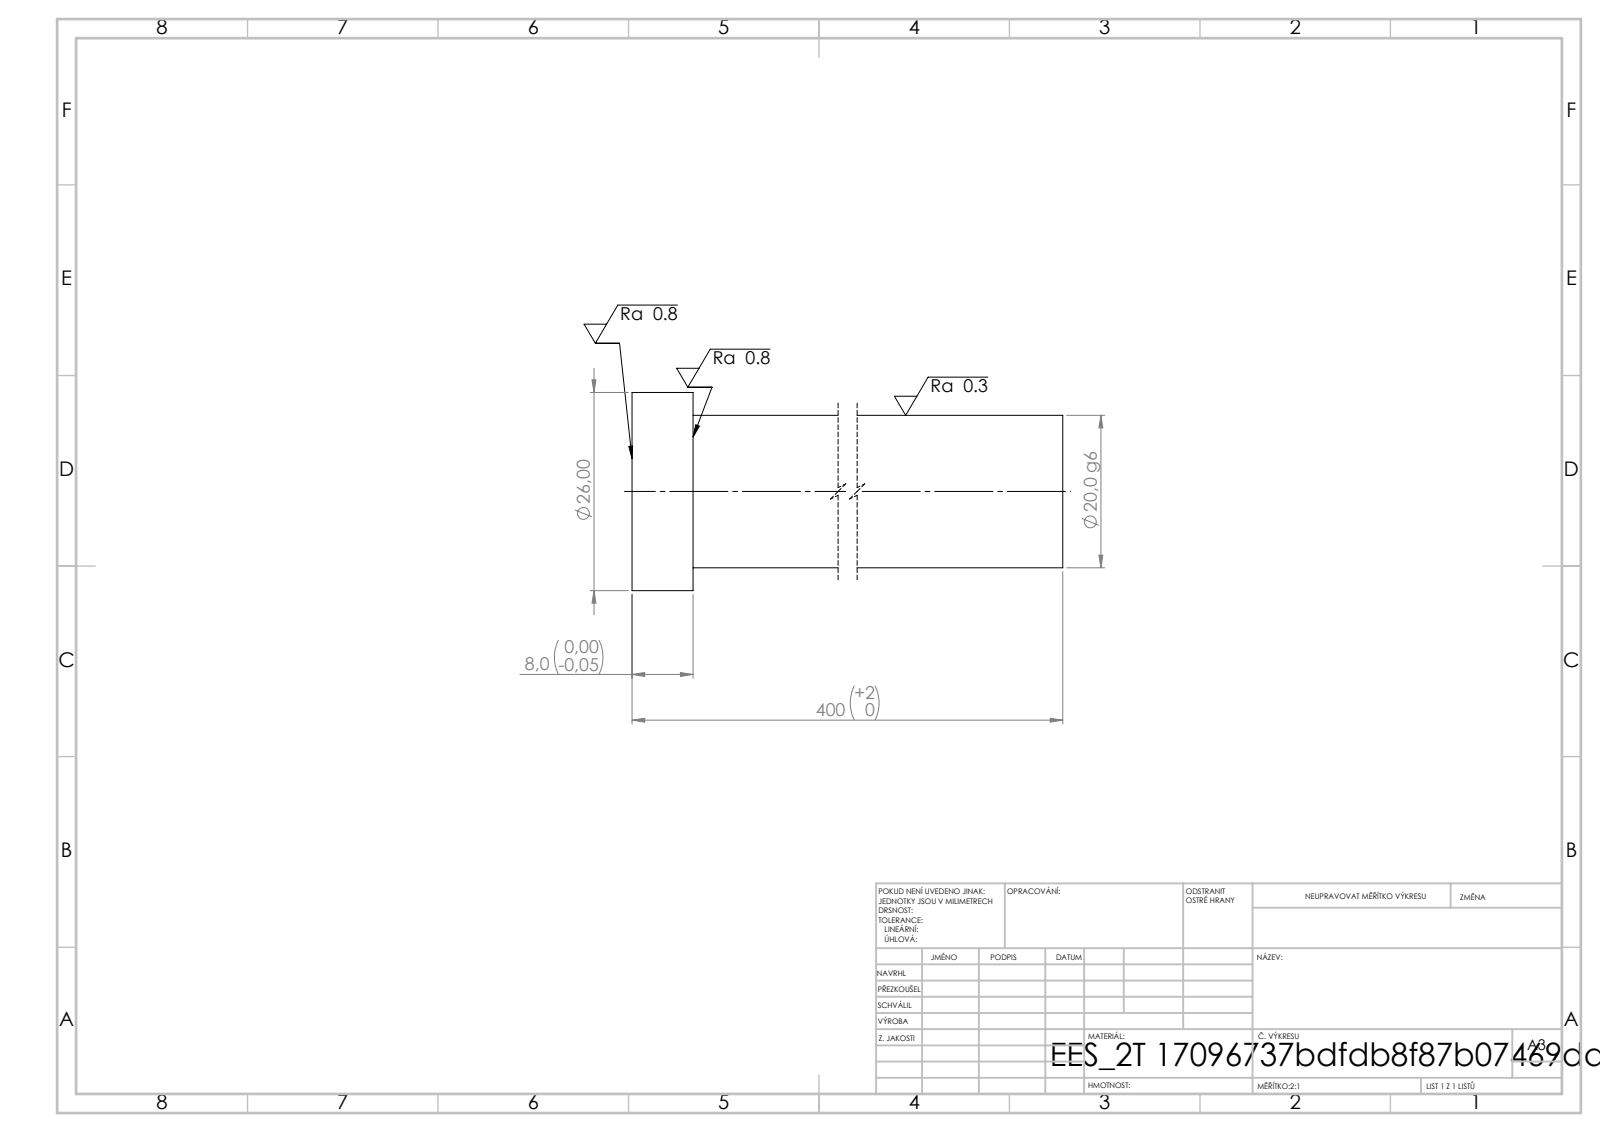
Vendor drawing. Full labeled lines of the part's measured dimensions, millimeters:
STEP written by: SolidWorks 2019 (CONFIG_CONTROL_DESIGN)
Units: millimetres
Bodies: 1 solid, 7 faces (3 planar, 4 cylindrical, 0 other)
Overall size (bounding box): 400 × 26 × 26
Volume: 127 398 mm³ · Surface area: 26 345 mm²
Round bosses / shafts (diameter × count): ⌀26 ×1, ⌀20 ×1
Main face-to-face distances: 400, 8, 392
